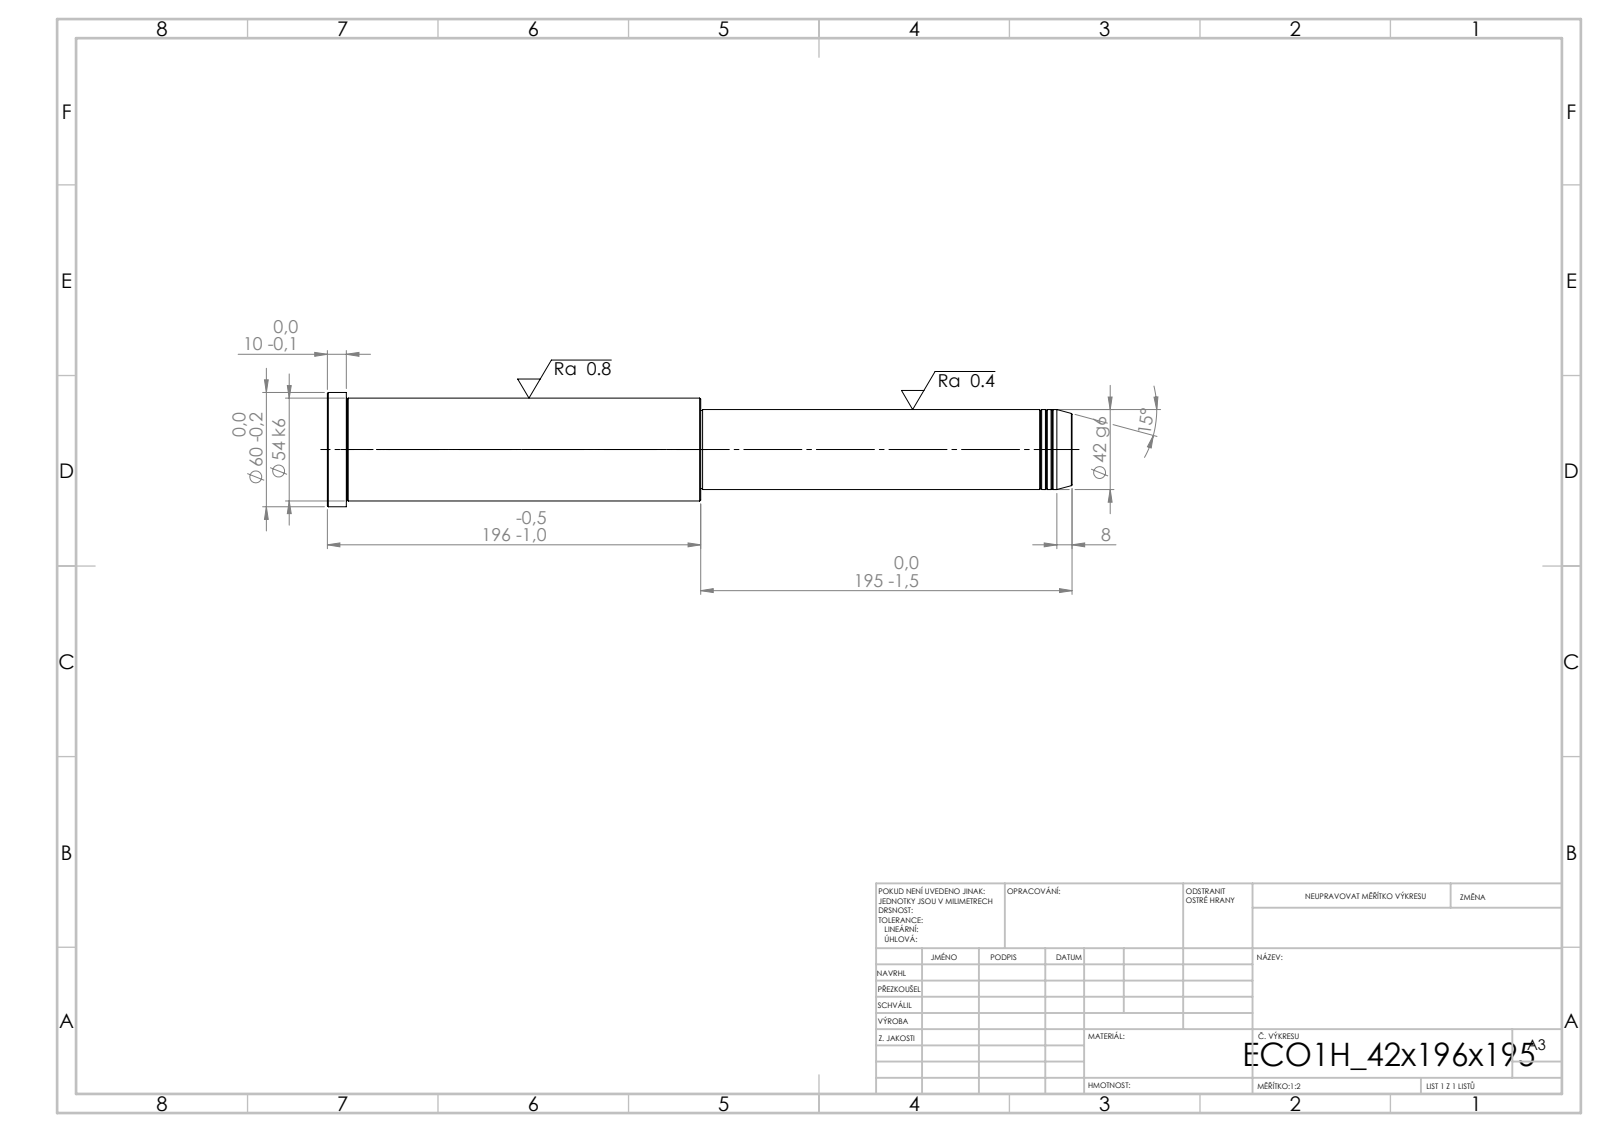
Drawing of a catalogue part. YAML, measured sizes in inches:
step_written_by: "SolidWorks 2019 (CONFIG_CONTROL_DESIGN)"
units: inches
bodies: {solids: 1, faces: 43, planar: 5, cylindrical: 14, other: 24}
overall_size: [15.394, 2.362, 2.362]
volume: 44.12
surface_area: 100.5
round_bosses_or_shafts:
  - {diameter: 2.362, count: 1}
  - {diameter: 2.126, count: 1}
  - {diameter: 1.654, count: 1}
  - {diameter: 1.614, count: 1}
face_to_face_distances: [15.394, 7.677, 7.717, 15, 7.323, 0.394, 7.638, 0.039, 7.362, 7.756]
